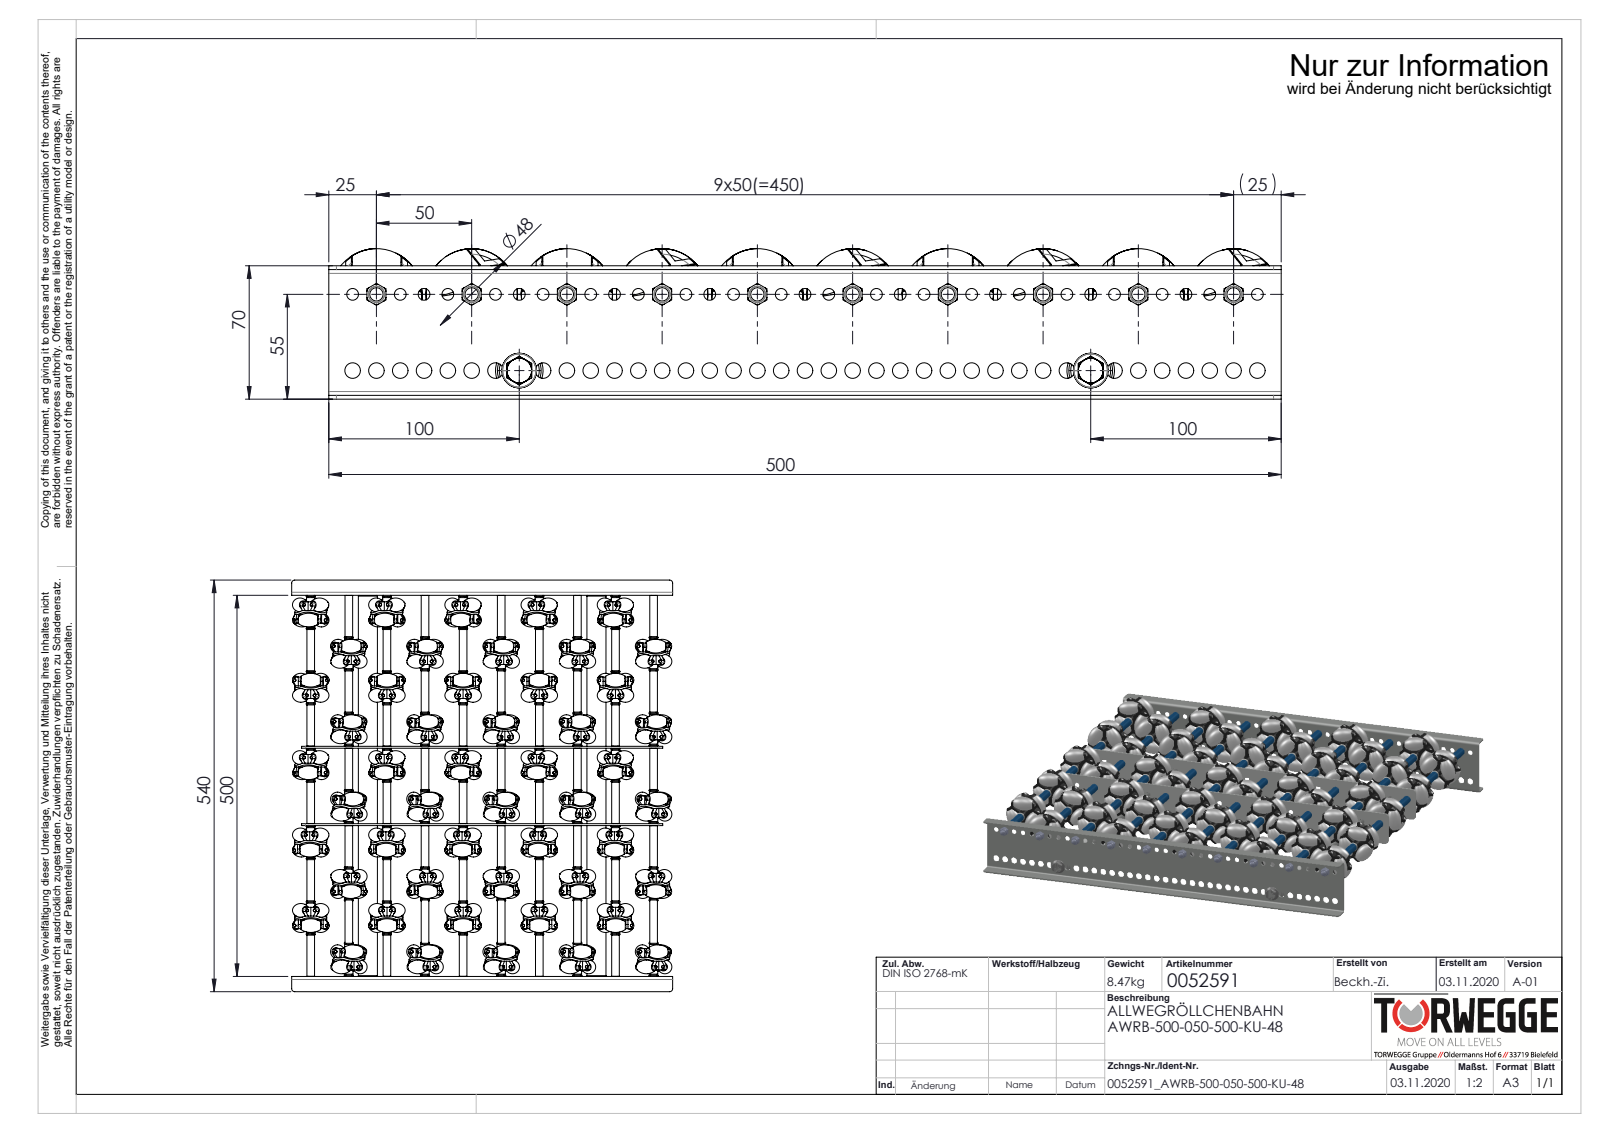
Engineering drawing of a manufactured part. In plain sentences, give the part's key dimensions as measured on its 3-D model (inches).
The part is named "S100994_Sperrzahnschraube_M08x16-8.8-A2K; AWR-Achse-für-Konfiguration_L500; AWR48_Halter; 0015028_AWR48 (+8 more)". Its 3-D file was written by "SolidWorks 2020 (AUTOMOTIVE_DESIGN)". It is 844 solids with 14948 faces: 5212 planar, 5752 cylindrical and 3984 other. Overall it measures 21.26 by 19.685 by 3.11 inches. Its volume is 174.7 cubic inches and its surface area 3 035 square inches. Round holes: 300 of diameter 0.146, 300 of diameter 0.165, 39 of diameter 0.244, 39 of diameter 0.323, 19 of diameter 0.256, 10 of diameter 0.194, 10 of diameter 0.331, 2 of diameter 0.268, 2 of diameter 0.827. Round bosses or shafts: 300 of diameter 0.157, 241 of diameter 0.146, 12 of diameter 0.315, 10 of diameter 1.654, 10 of diameter 0.433, 10 of diameter 0.394, 10 of diameter 0.276, 10 of diameter 0.236. Partial cylindrical surfaces (rounded edges, fillets, slot ends): 10 of radius 0.927, 8 of radius 0.157, 4 of radius 0.079, 4 of radius 0.197. The main face-to-face distances are 0.079, 19.764, 3.996, 0.098, 2.677, 19.685, 19.843, 0.118, 3.898, 7.969. The hole center spacings are 1.42, 1.419, 1.419, 0.492, 1.42, 3.445, 3.702, 2.988.
